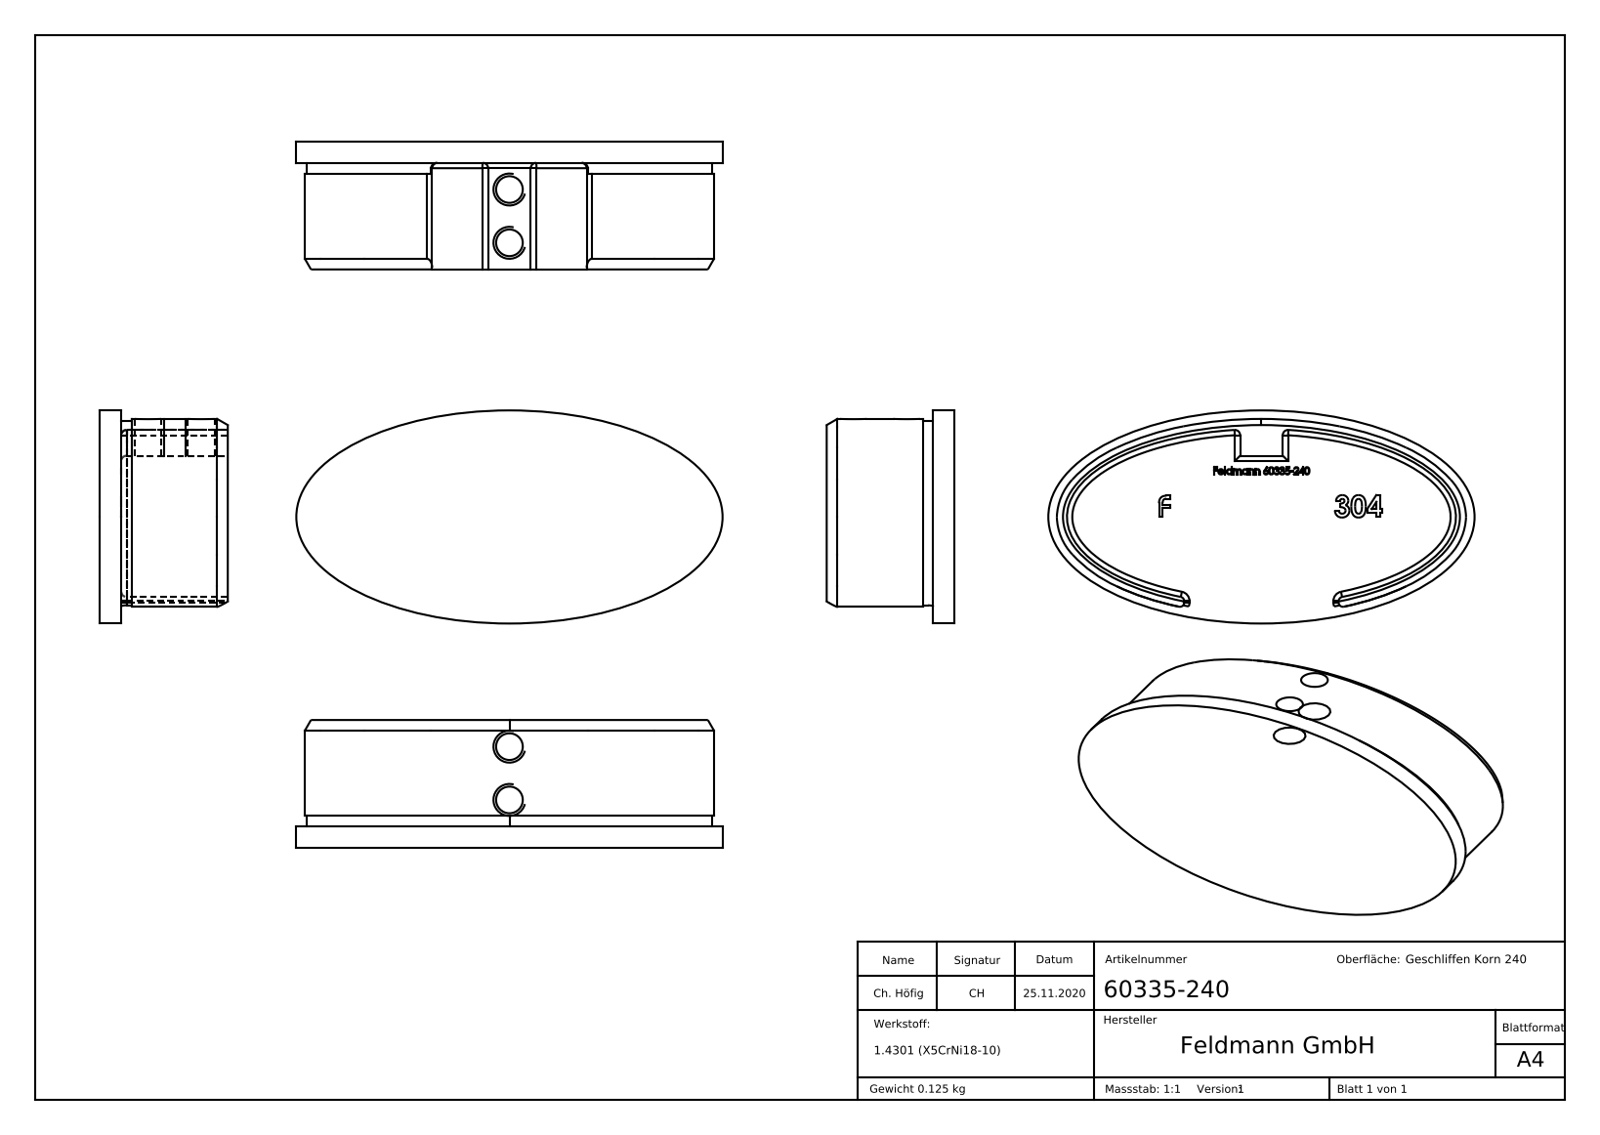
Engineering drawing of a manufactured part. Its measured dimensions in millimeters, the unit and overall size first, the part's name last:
Units: millimetres
Overall size (bounding box): 80 × 40 × 24
Round holes (diameter × count): ⌀5 ×2
Partial cylindrical surfaces — rounded edges, fillets, slot ends (radius × count): R1 ×7, R0.8 ×4
Main face-to-face distances: 4, 20, 24, 8, 2, 18, 6, 2.1, 3.9, 20.1
Hole centre spacings: 10
Volume: 15 761 mm³ · Surface area: 12 057 mm²
Bodies: 1 solid, 338 faces (161 planar, 15 cylindrical, 162 other)
Part name (STEP PRODUCT): 60335-240
STEP written by: SolidWorks 2018 (CONFIG_CONTROL_DESIGN)
